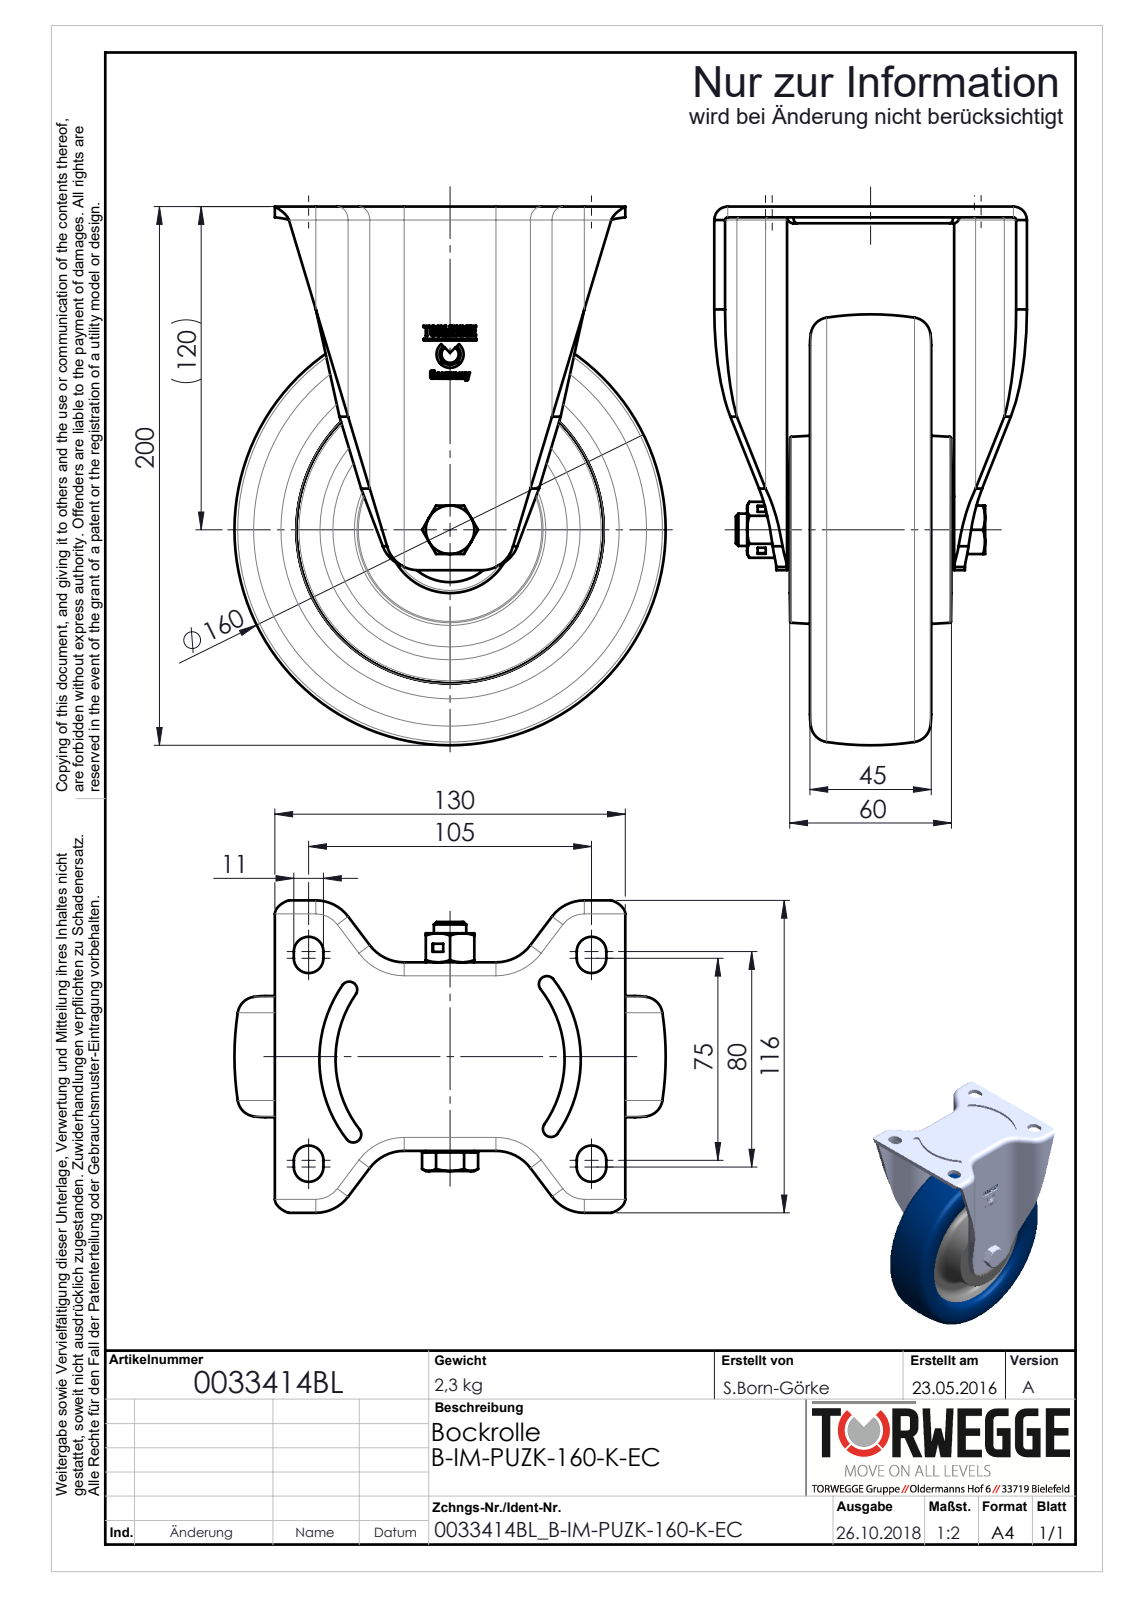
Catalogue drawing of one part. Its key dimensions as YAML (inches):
part_name: "K0033414BL_B-IM-PUZK-160-K-EC"
step_written_by: "SolidWorks 2016 (AUTOMOTIVE_DESIGN)"
units: inches
bodies: {solids: 0, faces: 622, planar: 313, cylindrical: 163, other: 146}
overall_size: [7.874, 6.299, 4.567]
round_holes:
  - {diameter: 0.402, count: 1}
  - {diameter: 0.472, count: 1}
  - {diameter: 0.48, count: 1}
  - {diameter: 0.787, count: 1}
  - {diameter: 0.807, count: 1}
  - {diameter: 1.531, count: 1}
round_bosses_or_shafts:
  - {diameter: 1.106, count: 1}
  - {diameter: 0.984, count: 1}
  - {diameter: 0.783, count: 1}
  - {diameter: 0.709, count: 1}
partial_cylinders:
  - {radius: 0.015, count: 8}
  - {radius: 0.039, count: 8}
  - {radius: 0.197, count: 8}
  - {radius: 0.217, count: 8}
  - {radius: 0.008, count: 7}
  - {radius: 0.024, count: 7}
  - {radius: 0.005, count: 4}
  - {radius: 0.034, count: 4}
face_to_face_distances: [0.157, 2.598, 2.441, 0.787, 2.756, 1.181, 0.394, 1.024, 1.575, 1.417]
